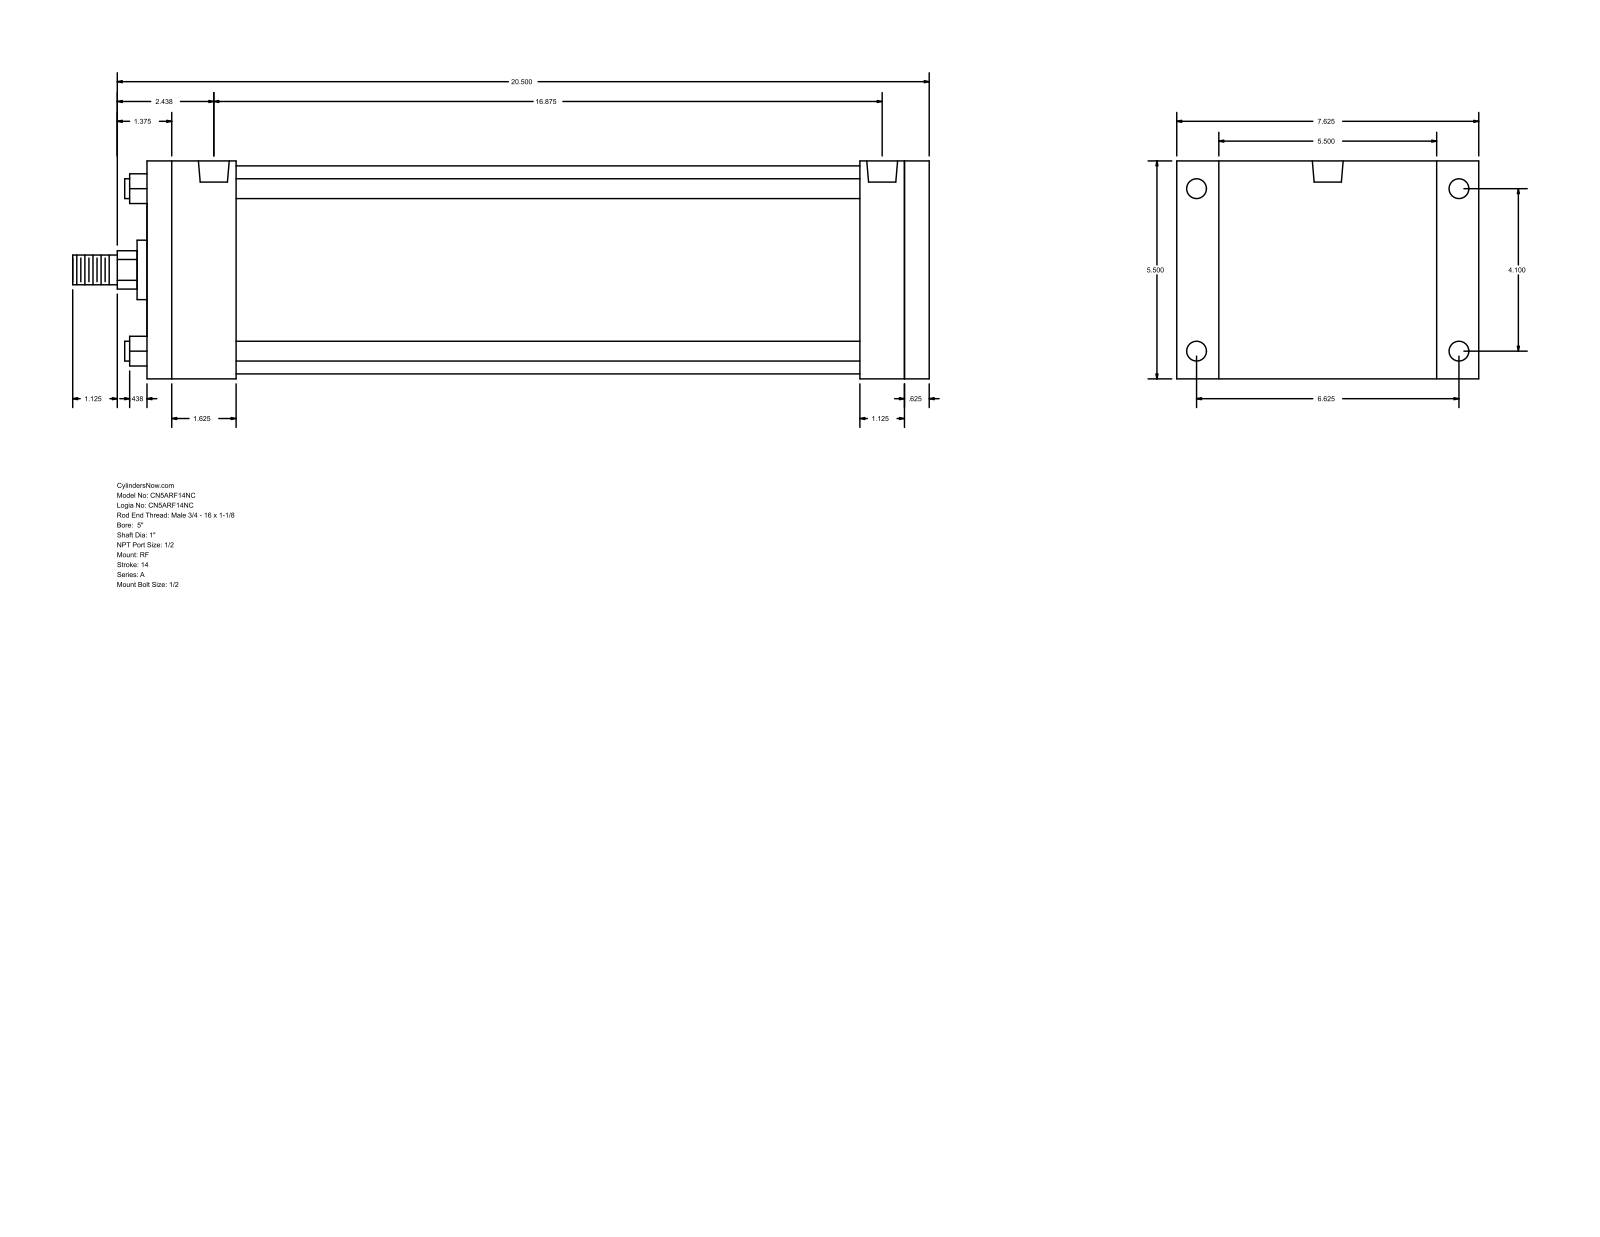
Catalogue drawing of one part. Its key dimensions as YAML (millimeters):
part_name: "A_RF__0500_1"
step_written_by: "GSSL Pune (CONFIG_CONTROL_DESIGN)"
units: millimeters
bodies: {solids: 0, faces: 92, planar: 64, cylindrical: 28, other: 0}
overall_size: [549.27, 193.68, 139.7]
round_holes:
  - {diameter: 8.73, count: 4}
  - {diameter: 12.7, count: 4}
  - {diameter: 19.77, count: 2}
round_bosses_or_shafts:
  - {diameter: 12.7, count: 4}
  - {diameter: 133.35, count: 1}
  - {diameter: 38.1, count: 1}
  - {diameter: 25.4, count: 1}
  - {diameter: 19.05, count: 1}
partial_cylinders:
  - {radius: 12.29, count: 1}
face_to_face_distances: [139.7, 501.65, 485.77, 15.88, 28.57, 57.15, 428.62, 444.5, 457.2, 400.05]
hole_center_spacings: [2.39, 104.14, 168.28, 197.9, 423.85, 426.24, 428.63]
